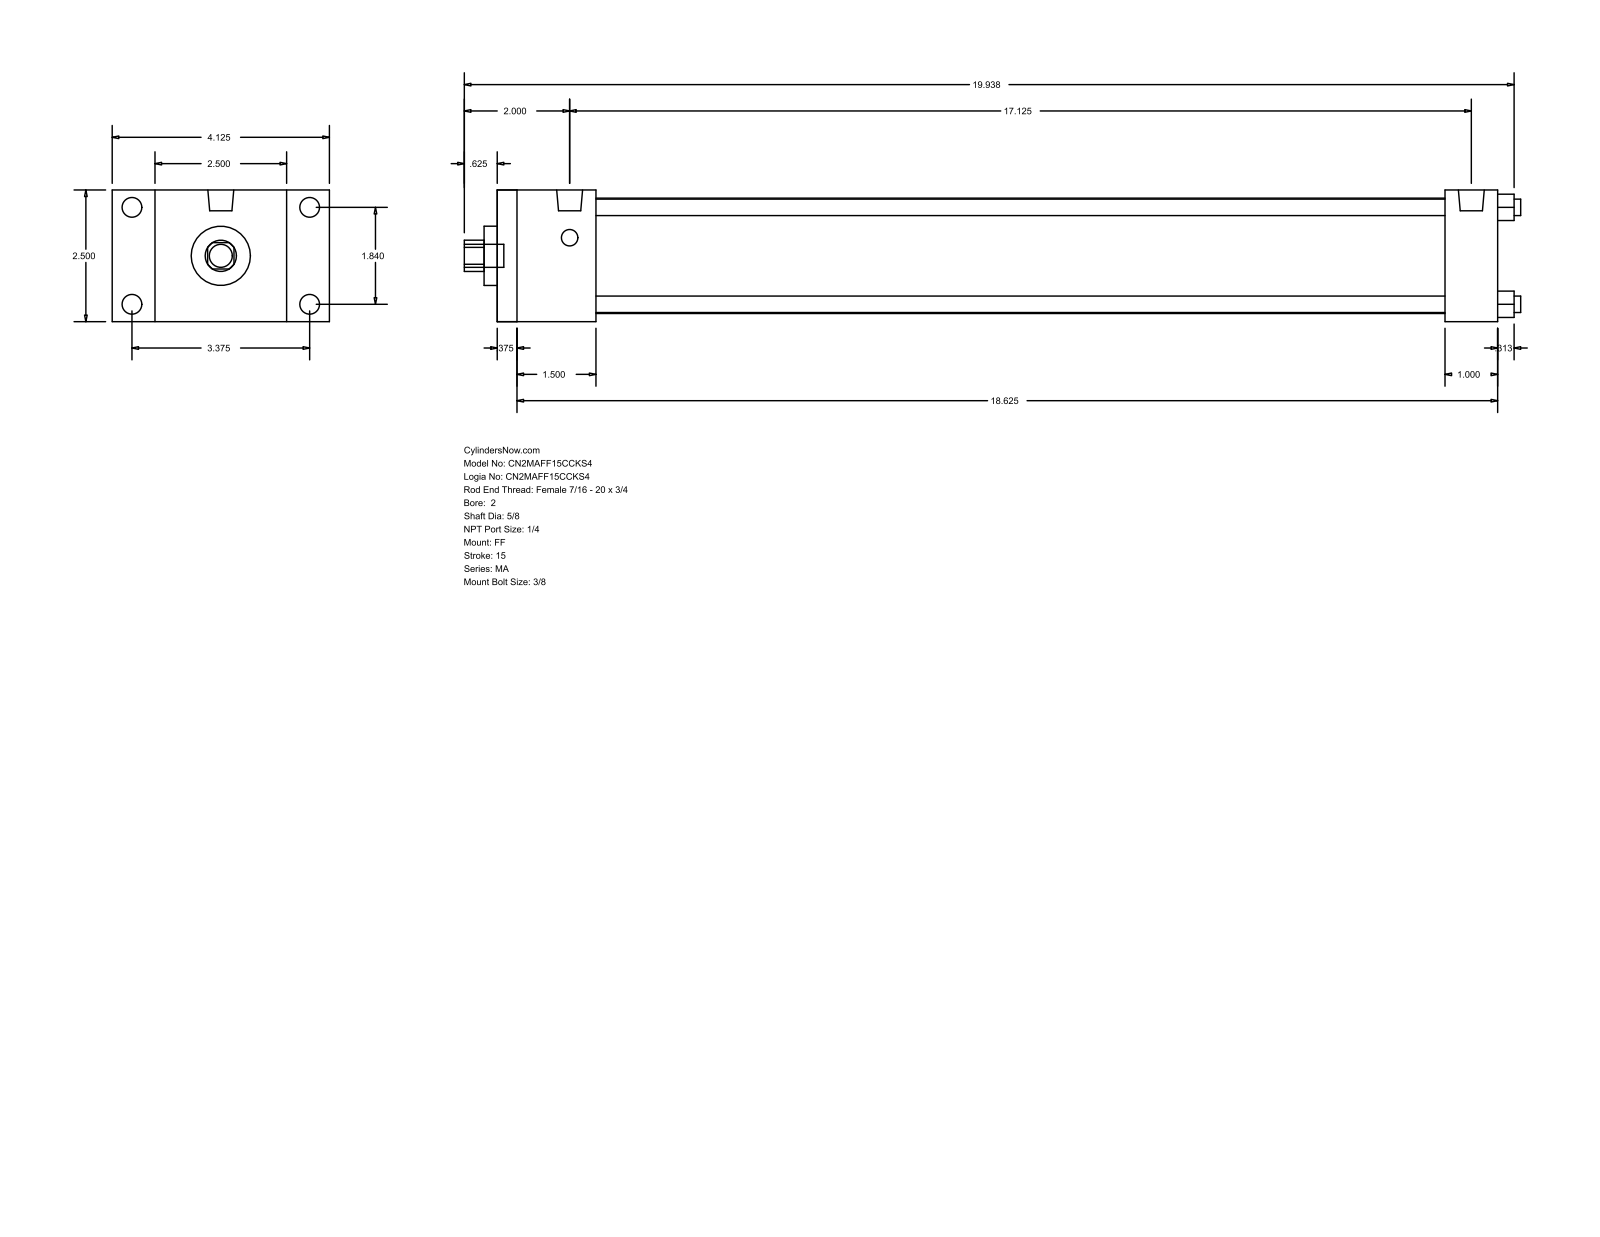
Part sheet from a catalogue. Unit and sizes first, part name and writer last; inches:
Units: inches
Overall size (bounding box): 20.063 × 4.125 × 2.5
Round holes (diameter × count): ⌀0.313 ×4, ⌀0.625 ×1, ⌀1.125 ×1, ⌀2.19 ×1
Round bosses / shafts (diameter × count): ⌀0.375 ×4, ⌀0.313 ×4, ⌀0.492 ×2, ⌀0.437 ×1
Partial cylindrical surfaces — rounded edges, fillets, slot ends (radius × count): R0.297 ×1
Main face-to-face distances: 2.5, 19, 0.375, 18.625, 1.5, 1.875, 18, 17.625, 16.125, 17.125
Hole centre spacings: 1.301, 1.84, 2.602
Bodies: 0 solids, 92 faces (64 planar, 28 cylindrical, 0 other)
Part name (STEP PRODUCT): MA_FF__0200_0.625
STEP written by: GSSL Pune (CONFIG_CONTROL_DESIGN)
